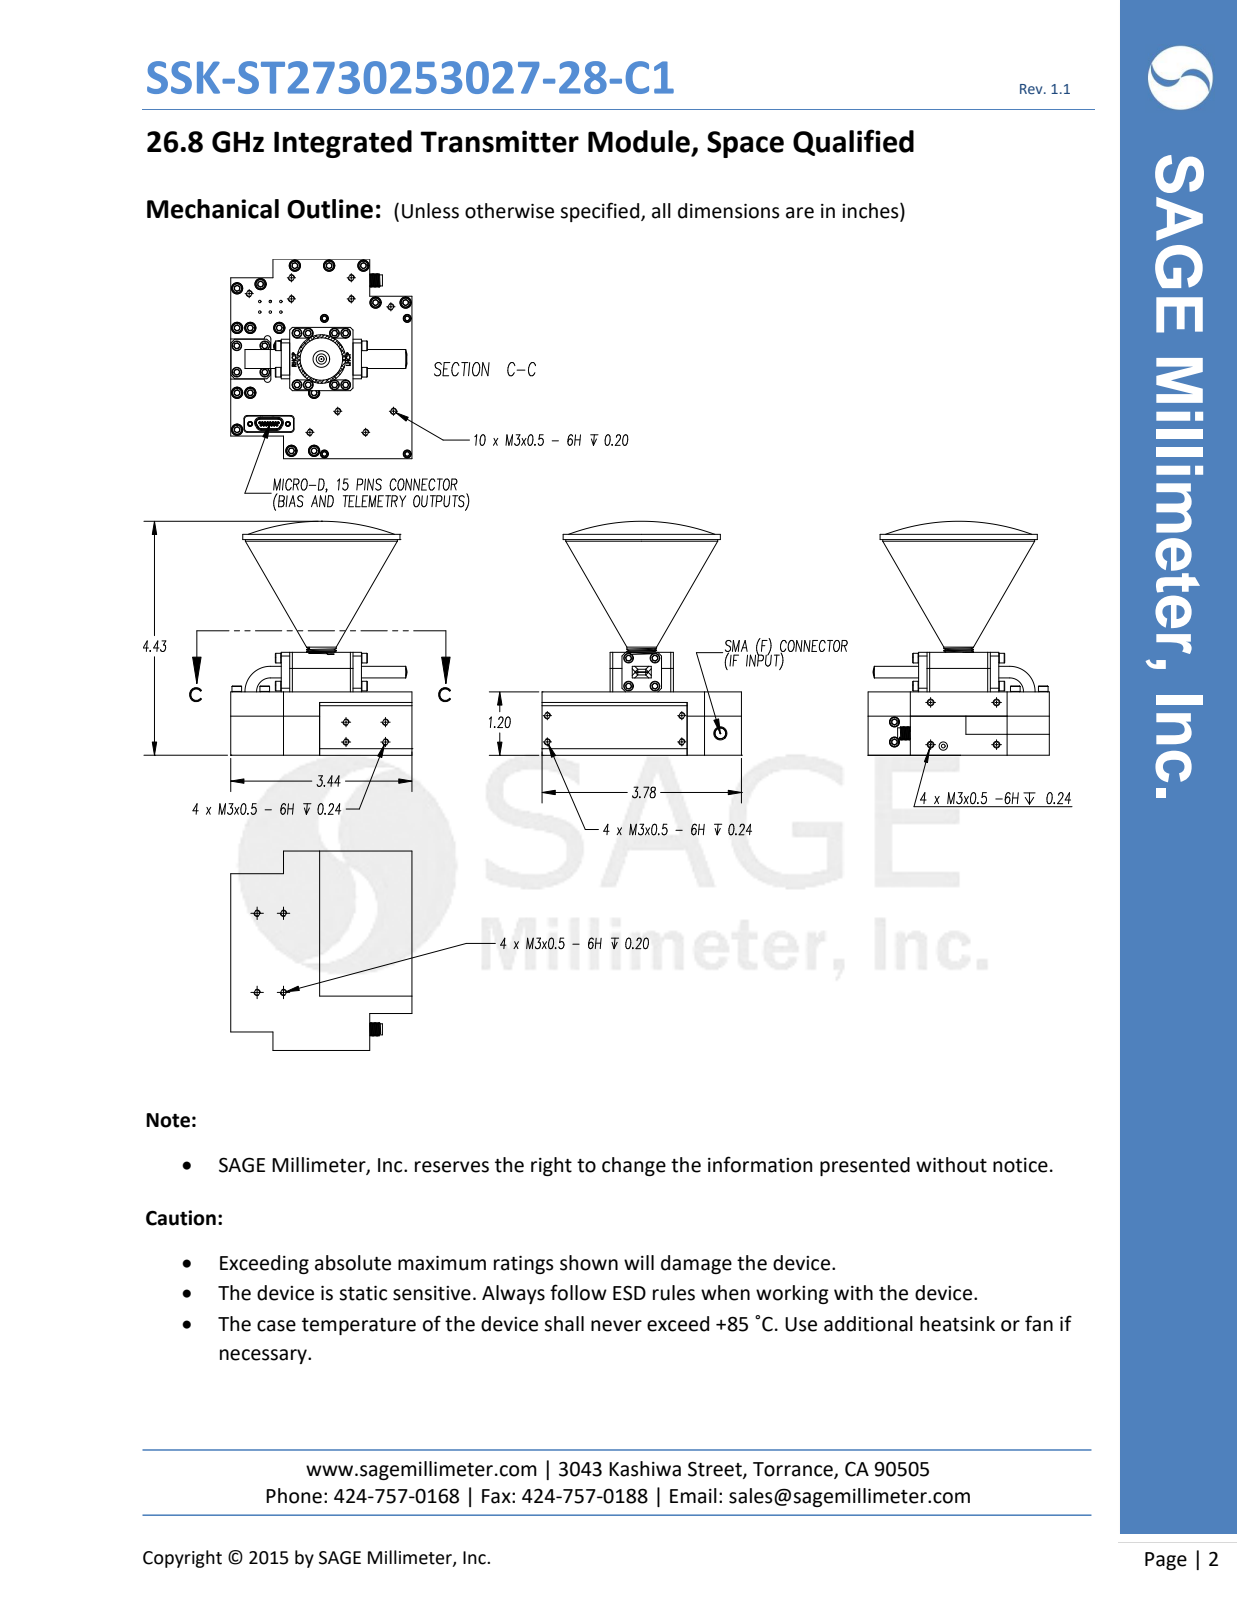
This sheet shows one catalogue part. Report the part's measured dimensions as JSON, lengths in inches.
{"part_name": "SSK-ST2730253027-28-C1", "step_written_by": "SolidWorks 2016 (CONFIG_CONTROL_DESIGN)", "units": "inches", "bodies": {"solids": 29, "faces": 1555, "planar": 445, "cylindrical": 599, "other": 511}, "overall_size": [3.78, 3.435, 1.202], "volume_in3": 12.92, "surface_area_in2": 119, "round_holes": [[0.098, 22], [0.125, 16], [0.213, 16], [0.036, 15], [0.043, 15], [0.089, 14], [0.047, 12], [0.025, 9], [0.126, 8], [0.025, 6], [0.047, 6], [0.07, 6]], "round_bosses_or_shafts": [[0.112, 17], [0.183, 15], [0.039, 15], [0.02, 15], [0.14, 4], [0.086, 4], [0.21, 1]], "partial_cylinders_radius": [[0.062, 10], [0.03, 4], [0.041, 4], [0.041, 4], [0.05, 4], [0.062, 4], [0.066, 4], [0.093, 4]], "face_to_face_distances": [0.2, 0.46, 0.26, 0.617, 0.877, 1.077, 0.198, 0.815, 0.062, 0.262], "hole_center_spacings": [0.05, 0.087, 0.1, 0.132, 0.15, 0.2, 0.18, 0.25]}
